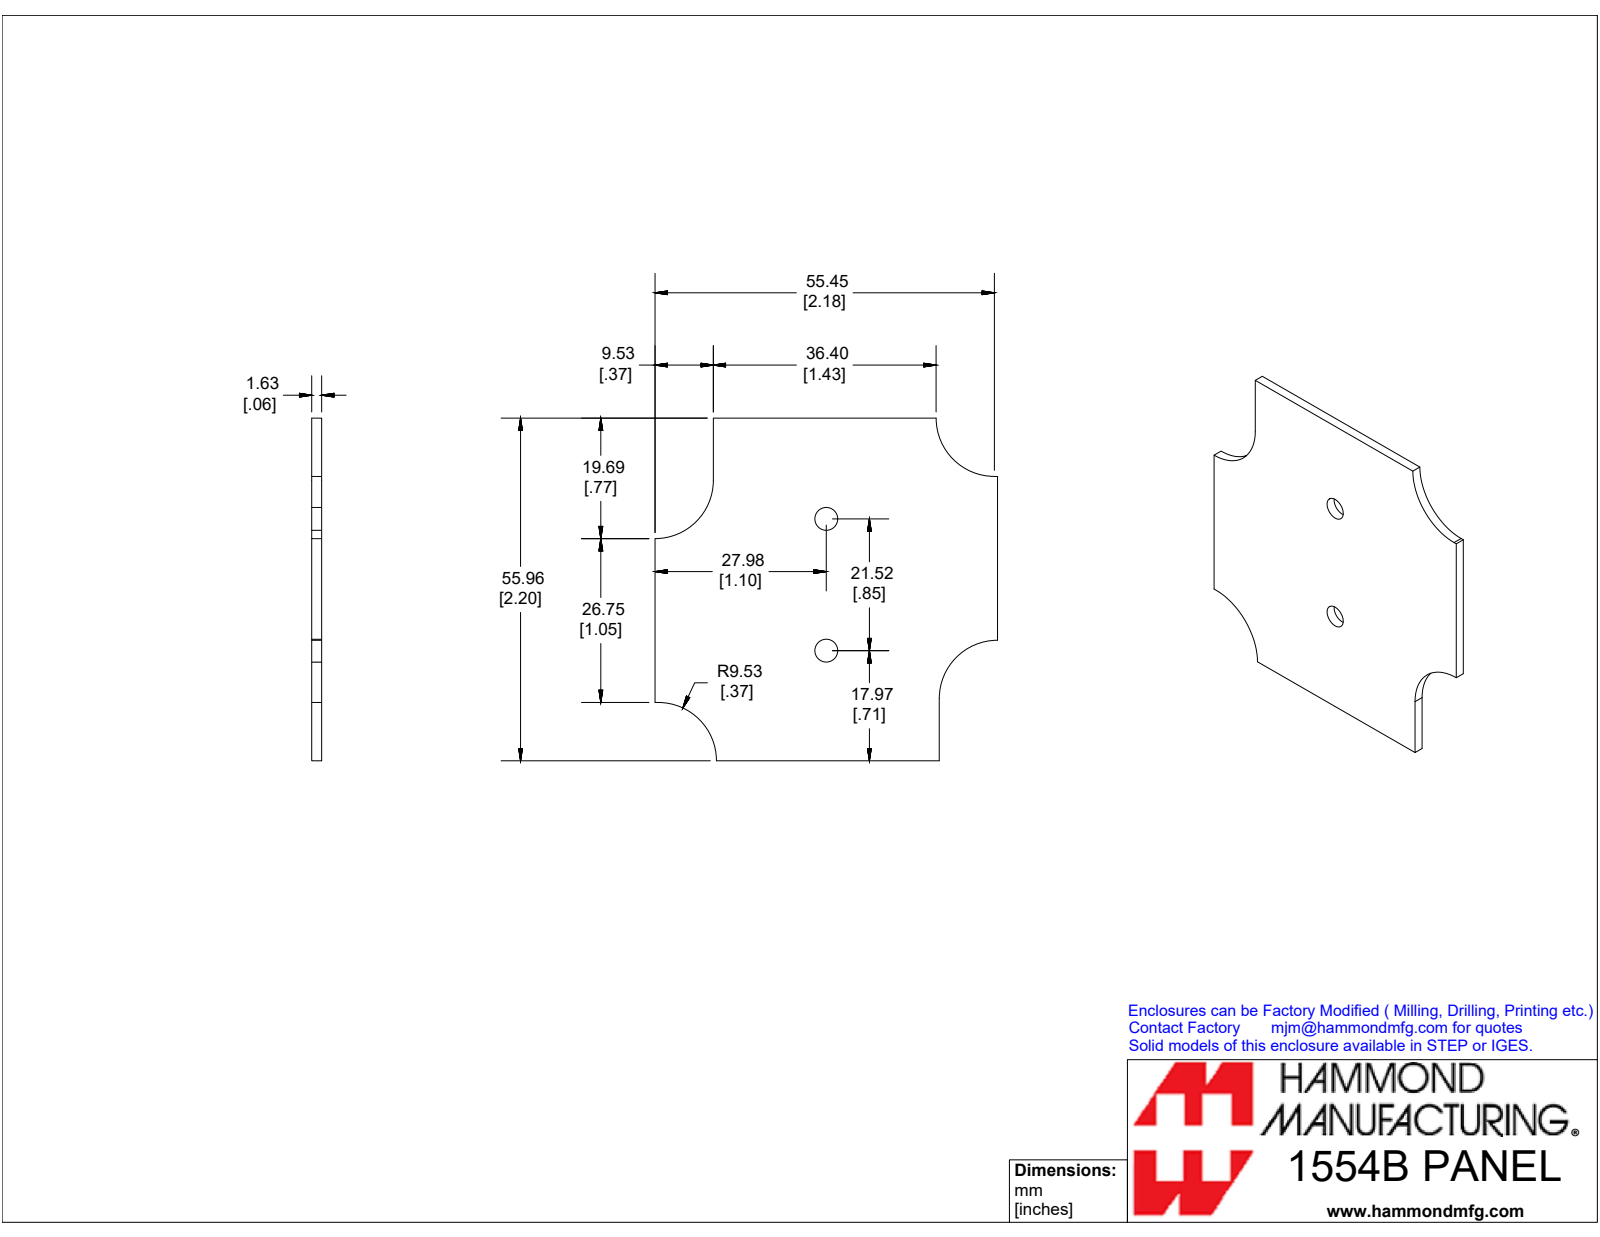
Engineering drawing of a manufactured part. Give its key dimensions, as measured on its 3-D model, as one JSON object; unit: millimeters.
{"part_name": "1554BPL", "step_written_by": "SolidWorks 2019 (CONFIG_CONTROL_DESIGN)", "units": "millimeters", "bodies": {"solids": 1, "faces": 16, "planar": 10, "cylindrical": 6, "other": 0}, "overall_size": [56, 56, 1.6], "volume_mm3": 4260, "surface_area_mm2": 5617, "round_holes": [[3.7, 2]], "partial_cylinders_radius": [[9.5, 4]], "face_to_face_distances": [1.6, 56, 9.5, 46.4, 36.9], "hole_center_spacings": [21.5]}
